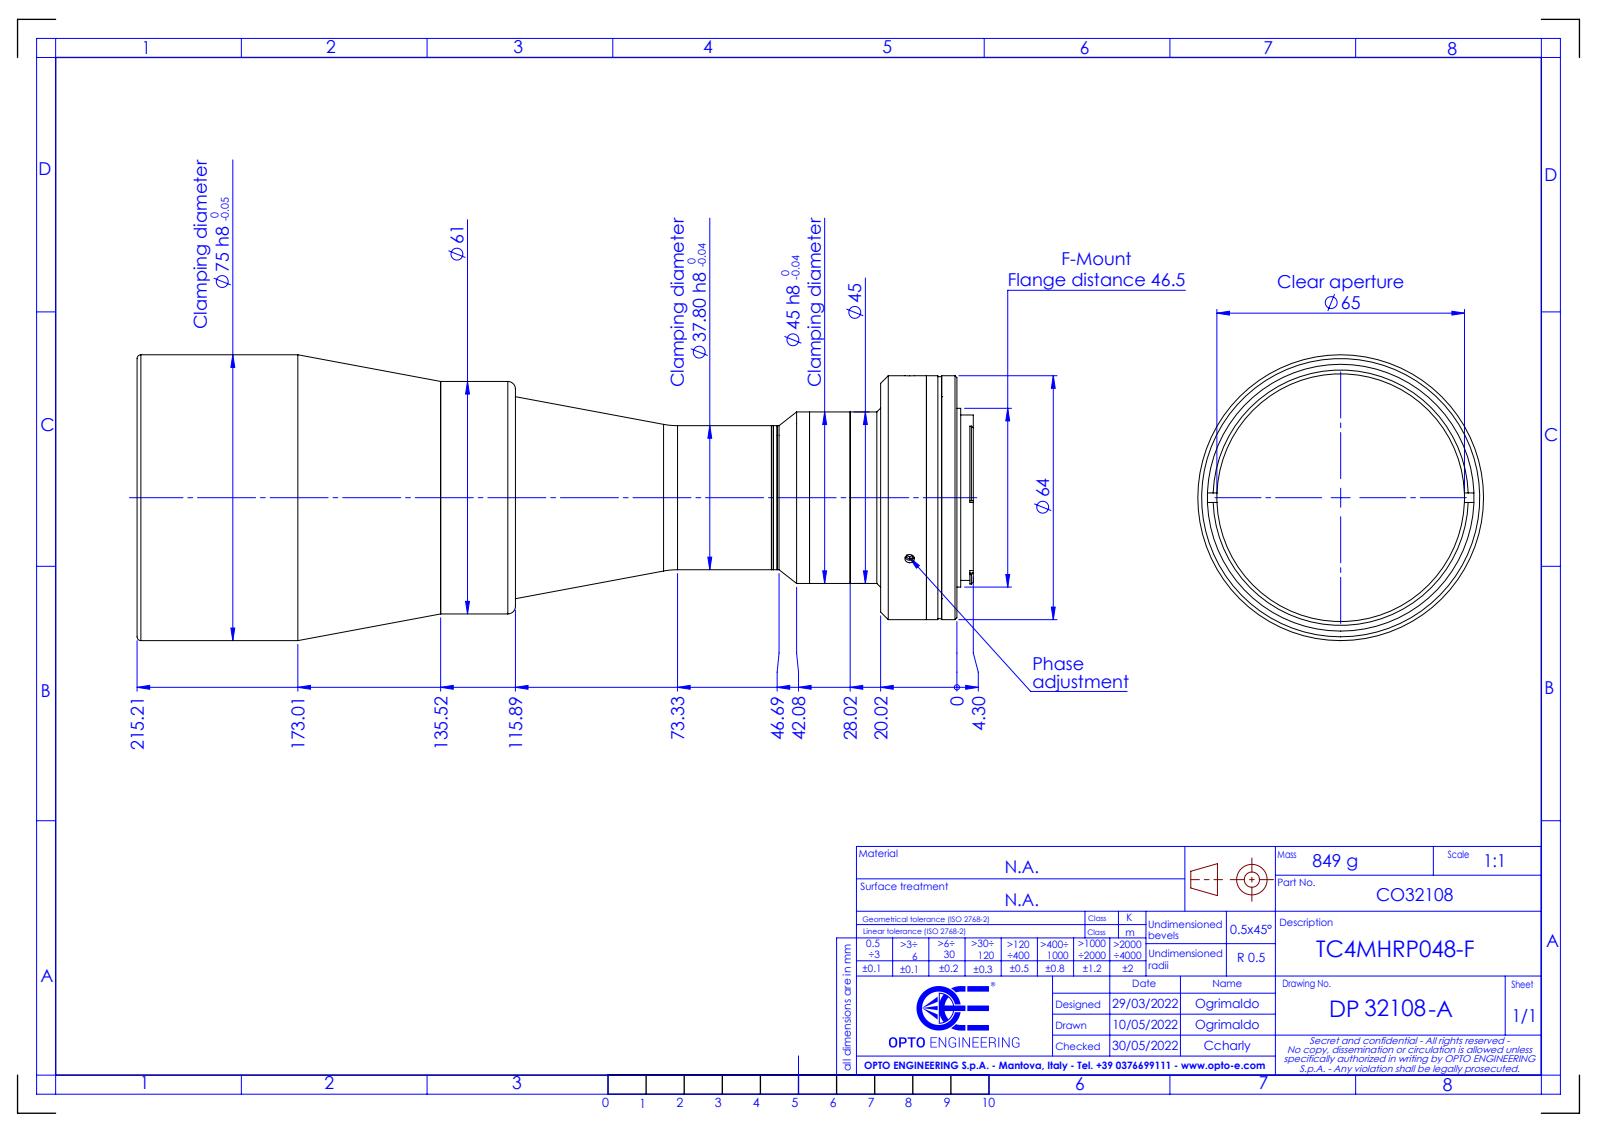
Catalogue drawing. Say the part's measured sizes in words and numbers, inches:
The part is named "DP32108-A_TC4MHRP048-F". Its 3-D file was written by "SolidWorks 2021 (CONFIG_CONTROL_DESIGN)". It is 0 solids with 144 faces: 48 planar, 62 cylindrical and 34 other. Overall it measures 8.642 by 2.953 by 2.953 inches. Round holes: 3 of diameter 0.098, 1 of diameter 1.142, 1 of diameter 1.26, 1 of diameter 1.654, 1 of diameter 2.087, 1 of diameter 2.559, 1 of diameter 2.756. Round bosses or shafts: 1 of diameter 2.953, 1 of diameter 2.52, 1 of diameter 2.5, 1 of diameter 2.402, 1 of diameter 1.846, 1 of diameter 1.772, 1 of diameter 1.709, 1 of diameter 1.488. Partial cylindrical surfaces (rounded edges, fillets, slot ends): 5 of radius 0.02, 2 of radius 0.045, 1 of radius 0.892. The main face-to-face distances are 0.157, 0.197, 0.315, 0.039, 0.118, 0.788, 0.473, 0.591, 0.631, 4.547.
